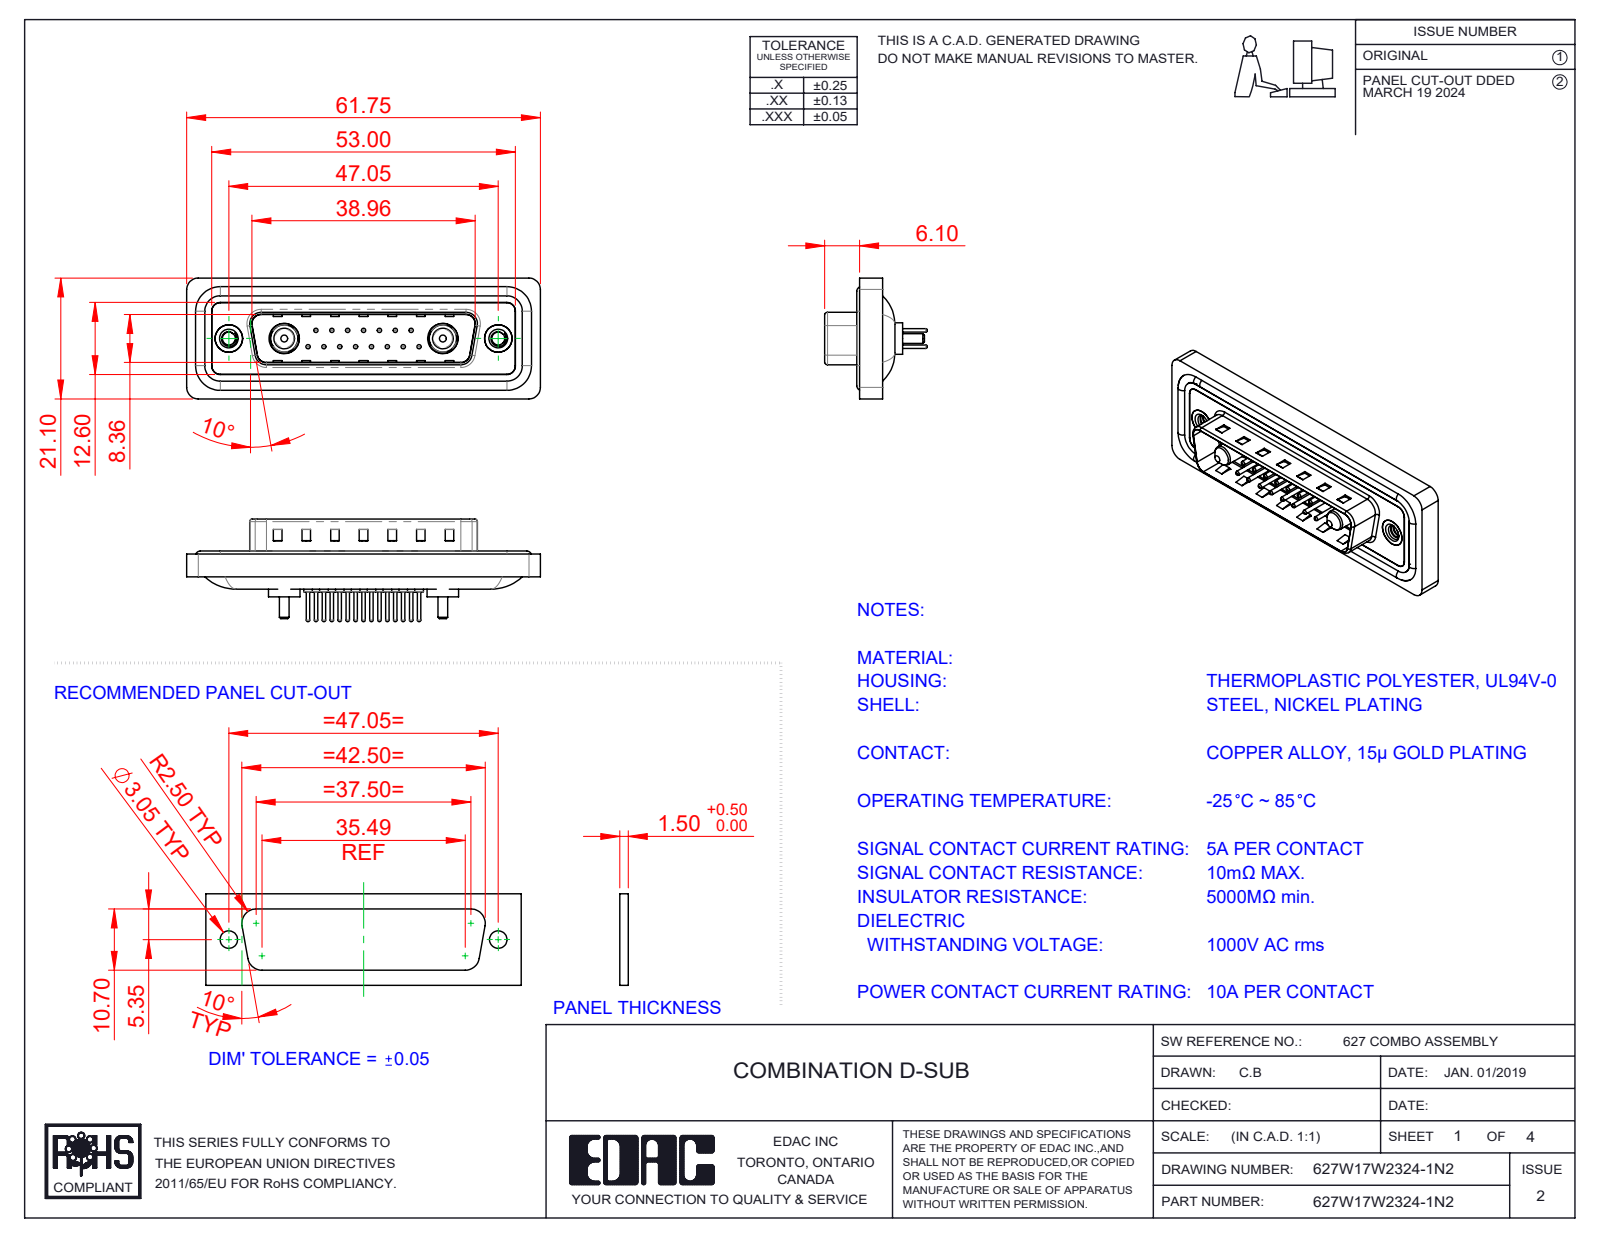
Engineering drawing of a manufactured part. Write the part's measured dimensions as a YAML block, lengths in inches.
part_name: "627W17W2324-1N2; 627Combo Housing_17W2; 627Combo Contact Row 1_24; 627Combo Shell Front_25 Contacts (+5 more)"
step_written_by: "SolidWorks 2023 (CONFIG_CONTROL_DESIGN)"
units: inches
bodies: {solids: 26, faces: 1116, planar: 334, cylindrical: 436, other: 346}
overall_size: [2.431, 0.831, 0.705]
volume: 0.442
surface_area: 18.43
round_holes:
  - {diameter: 0.03, count: 15}
  - {diameter: 0.063, count: 15}
  - {diameter: 0.079, count: 15}
  - {diameter: 0.089, count: 2}
  - {diameter: 0.157, count: 2}
  - {diameter: 0.189, count: 2}
  - {diameter: 0.191, count: 2}
  - {diameter: 0.197, count: 2}
  - {diameter: 0.209, count: 2}
round_bosses_or_shafts:
  - {diameter: 0.059, count: 15}
  - {diameter: 0.024, count: 15}
  - {diameter: 0.063, count: 4}
  - {diameter: 0.217, count: 2}
  - {diameter: 0.205, count: 2}
  - {diameter: 0.193, count: 2}
  - {diameter: 0.187, count: 2}
  - {diameter: 0.148, count: 2}
partial_cylinders:
  - {radius: 0.059, count: 22}
  - {radius: 0.079, count: 18}
  - {radius: 0.02, count: 8}
  - {radius: 0.063, count: 8}
  - {radius: 0.01, count: 4}
  - {radius: 0.024, count: 4}
  - {radius: 0.026, count: 4}
  - {radius: 0.035, count: 4}
face_to_face_distances: [0.016, 0.059, 0.043, 0.063, 0.02, 0.122, 0.114, 0.032, 0.377, 0.161]
hole_center_spacings: [0.124, 0.109, 0.218, 0.327, 0.198, 0.295, 0.436, 0.198]
